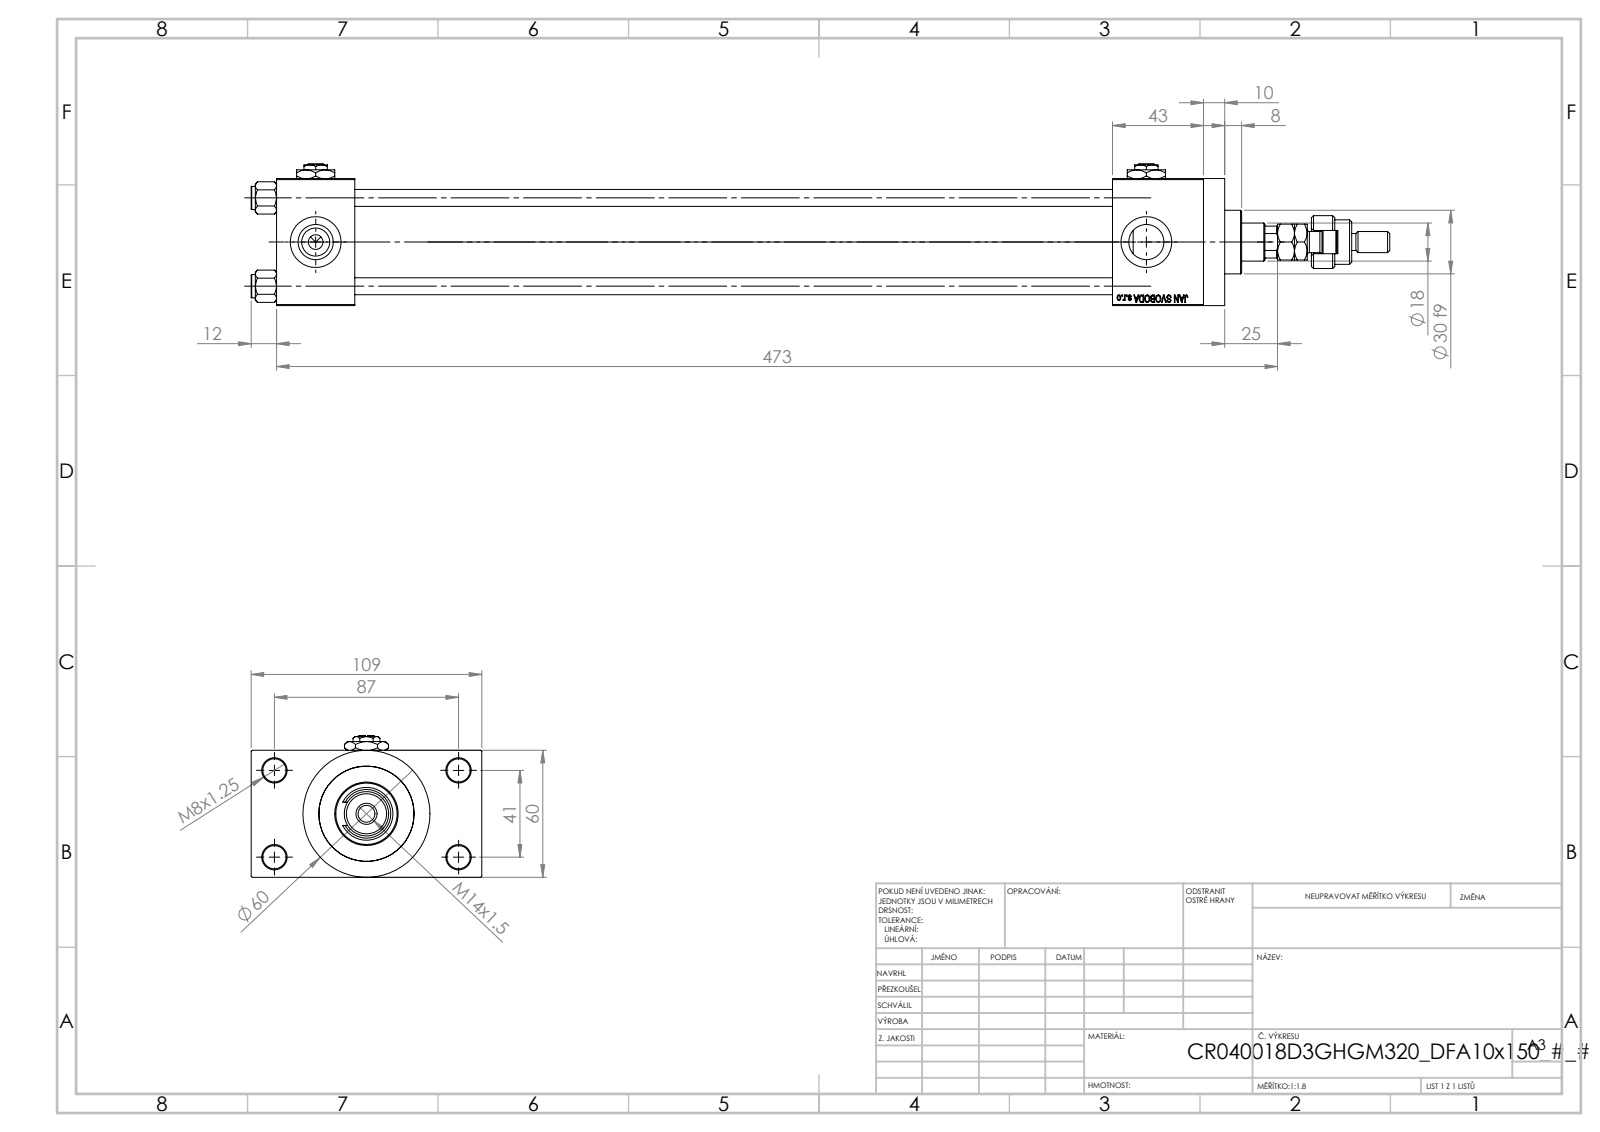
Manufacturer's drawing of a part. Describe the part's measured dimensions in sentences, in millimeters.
The part is named "MFA; V215_VC_A; FEMALE_PART_FOR_DFA; V215CR_D_Body (+4 more)". Its 3-D file was written by "SolidWorks 2019 (CONFIG_CONTROL_DESIGN)". It is 15 solids with 1290 faces: 574 planar, 112 cylindrical and 604 other. Overall it measures 538 by 109 by 67 millimeters. Its volume is 780 370 cubic millimeters and its surface area 258 814 square millimeters. Round holes: 4 of diameter 8, 4 of diameter 11, 4 of diameter 16.66, 4 of diameter 24, 3 of diameter 7, 1 of diameter 8.5, 1 of diameter 18, 1 of diameter 21, 1 of diameter 31, 1 of diameter 40, 1 of diameter 45. Round bosses or shafts: 4 of diameter 11, 1 of diameter 60, 1 of diameter 46, 1 of diameter 30, 1 of diameter 25, 1 of diameter 16, 1 of diameter 10, 1 of diameter 8. Partial cylindrical surfaces (rounded edges, fillets, slot ends): 1 of radius 5.5, 1 of radius 8.5, 1 of radius 8.75. The main face-to-face distances are 60, 24.5, 358, 84.5, 37, 395, 43, 438, 401, 53. The hole center spacings are 22.65, 29.49, 41.7, 47.15, 48.09, 64.35, 76.49, 41.
